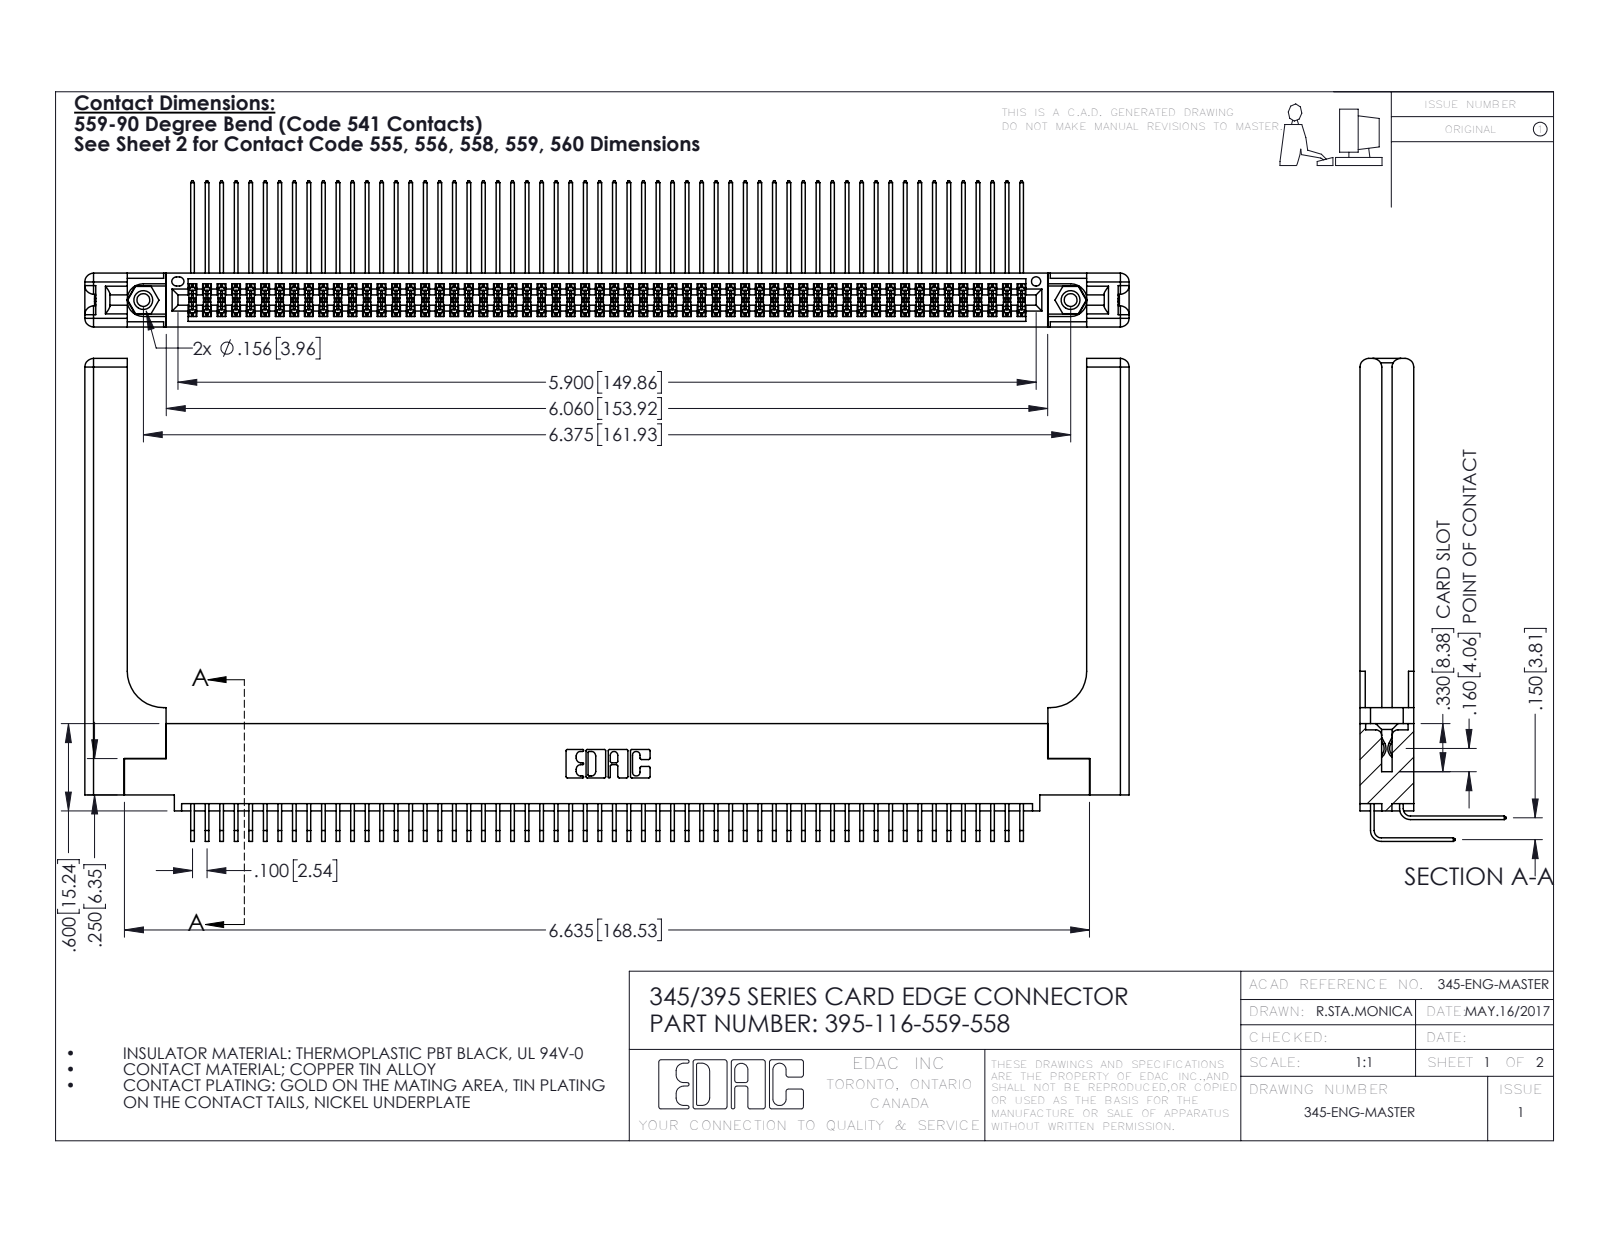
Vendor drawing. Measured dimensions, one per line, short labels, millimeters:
name: 345-250-001_345-250-001-102; 345-292-001_559 Tail - 2; 345 Part_0.110 Offset - 0.156 Dia-TH; 345-292-001_558 559 Tail - 1 (+2 more)
written by: SolidWorks 2016 (CONFIG_CONTROL_DESIGN)
unit: mm
bodies: 121 solids, 6418 faces (4292 planar, 2066 cylindrical, 60 other)
size: 182.3 × 84.3 × 25.5
volume: 26 940 mm³; area: 35 890 mm²
holes: 2× ⌀2.3, 2× ⌀3.2, 2× ⌀4, 1× ⌀1.6
bosses: 2× ⌀3.9
rounds: 174× R0.2, 22× R0.3, 16× R1.5, 6× R0.2, 6× R0.8, 3× R0.7, 2× R0.4, 2× R0.5
face distances: 1.8, 7.6, 9.4, 2.5, 6.9, 0.6, 5.1, 5.7, 4.4, 3.8
hole spacings: 6.9, 155.9, 161.9
